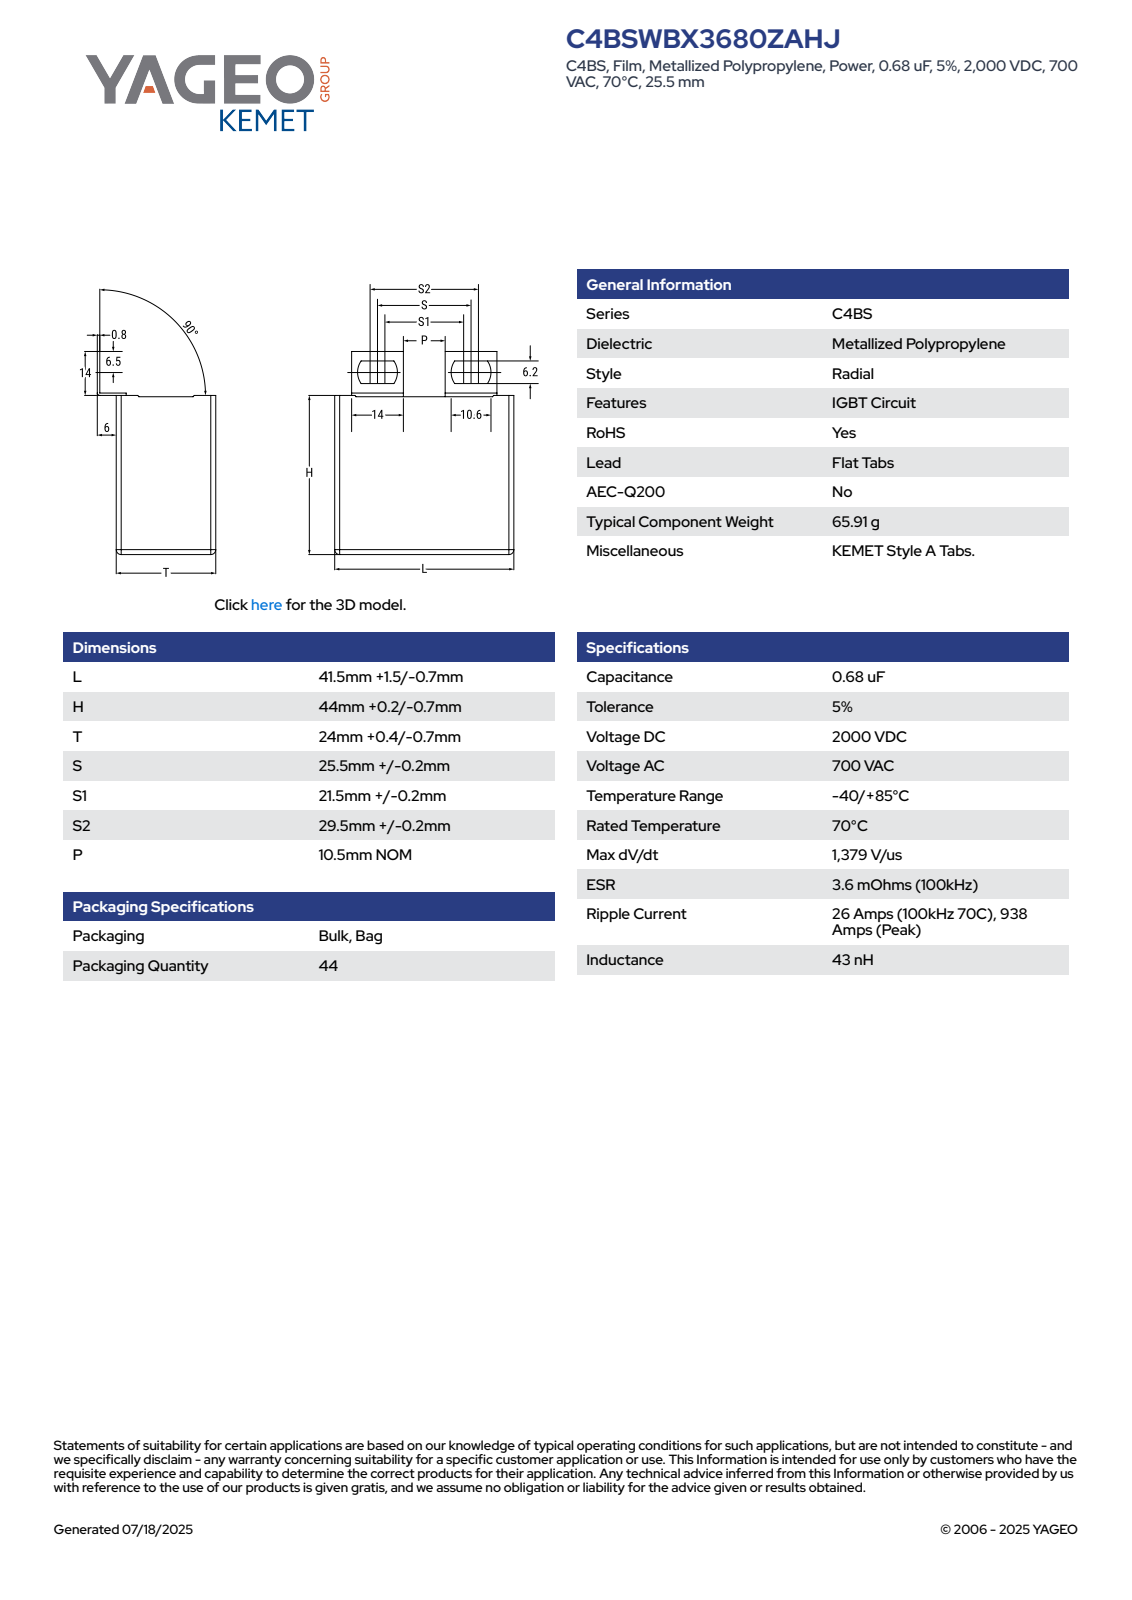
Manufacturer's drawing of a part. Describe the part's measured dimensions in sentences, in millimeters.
The part is named "CFP_C4BA_41.5X44X24_L43.5H44.2T24.4S25.7". Its 3-D file was written by "SolidWorks 2014 (AUTOMOTIVE_DESIGN)". It is 4 solids with 97 faces: 91 planar, 6 cylindrical and 0 other. Overall it measures 58.8 by 43.5 by 30.41 millimeters. Its volume is 47 301 cubic millimeters and its surface area 9 866 square millimeters. Partial cylindrical surfaces (rounded edges, fillets, slot ends): 4 of radius 6.1. The main face-to-face distances are 24.4, 43.5, 44.15, 0.6, 44.2, 44.8, 0.65, 30.4, 6, 29.8.
